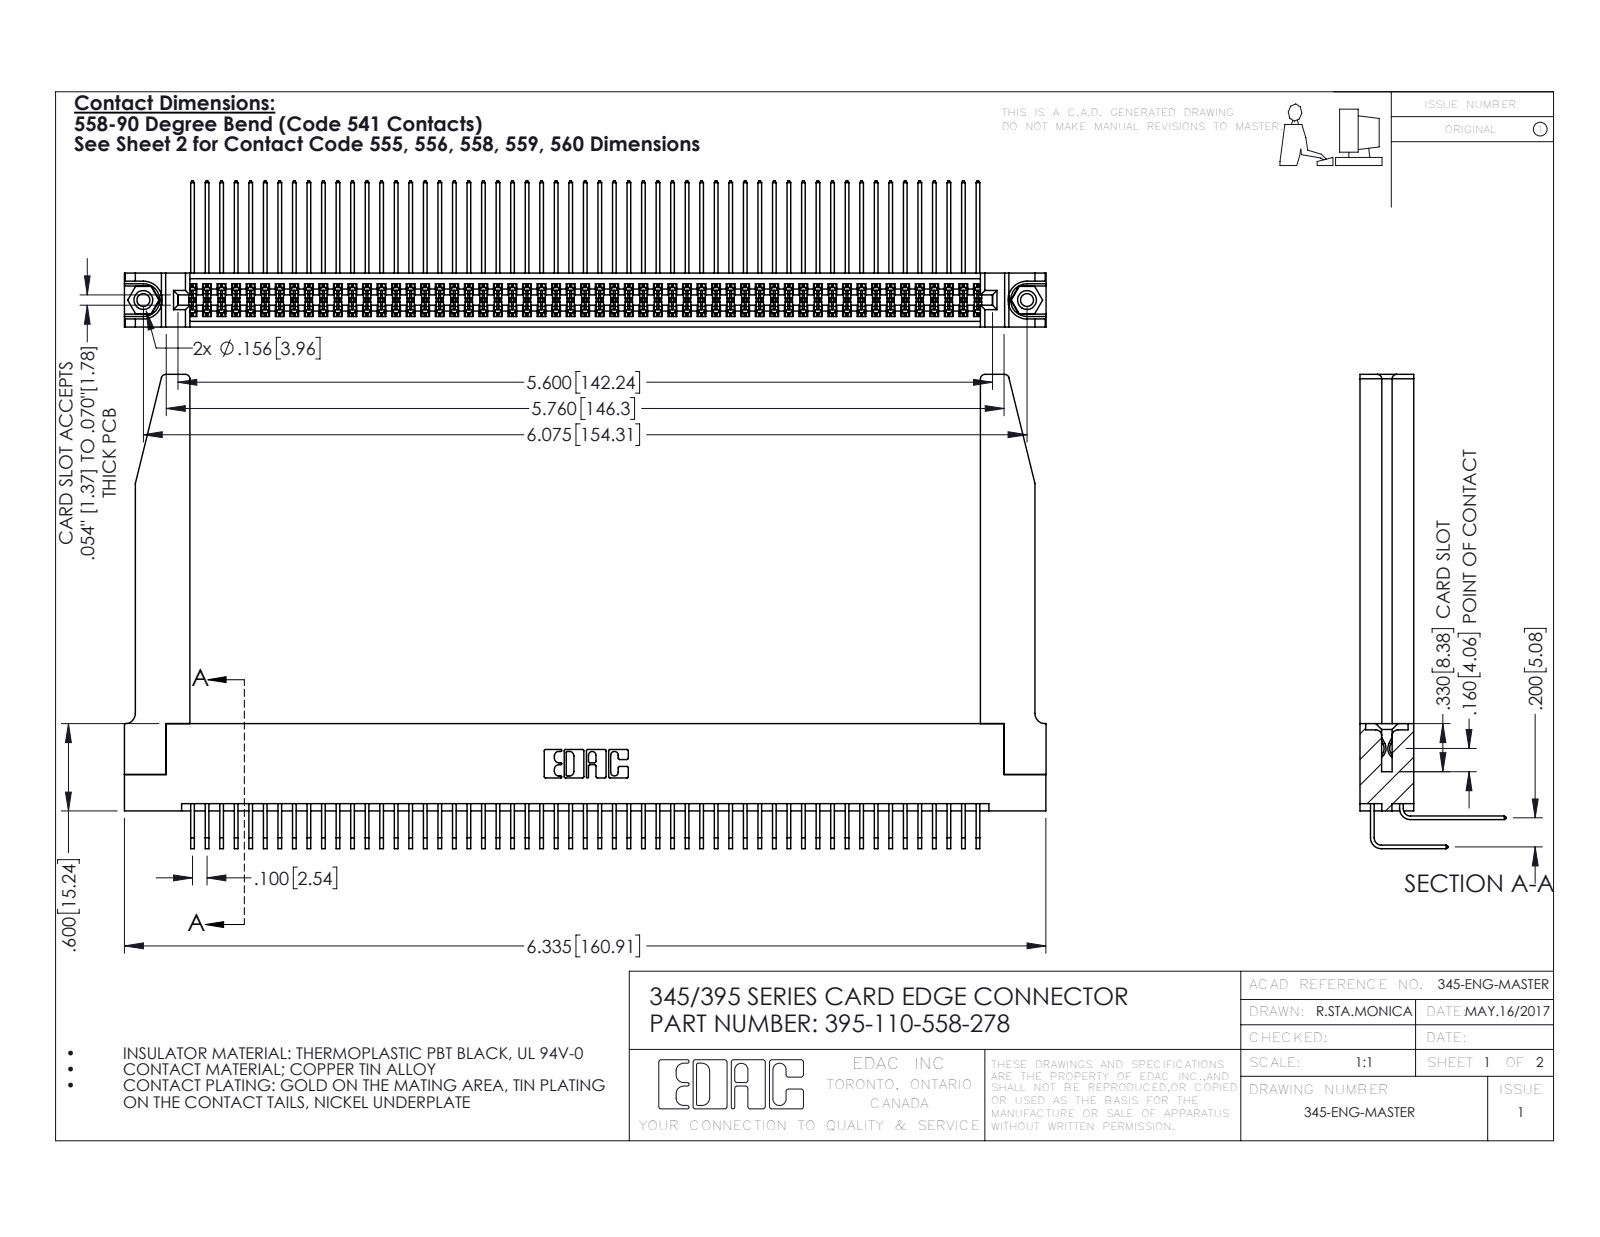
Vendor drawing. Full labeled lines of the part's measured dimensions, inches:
Part name (STEP PRODUCT): 345 Part_Flush Mounting Lugs - 0.156 Dia-TH; 345-220-078_345-220-078; 345-292-001_558 559 Tail - 1; 395-110-558-278 (+2 more)
STEP written by: SolidWorks 2016 (CONFIG_CONTROL_DESIGN)
Units: inches
Bodies: 115 solids, 6080 faces (4072 planar, 1956 cylindrical, 52 other)
Overall size (bounding box): 6.336 × 3.259 × 1.005
Volume: 1.474 in³ · Surface area: 53.16 in²
Round holes (diameter × count): ⌀0.089 ×2, ⌀0.125 ×2, ⌀0.156 ×2, ⌀0.064 ×1
Round bosses / shafts (diameter × count): ⌀0.155 ×2
Partial cylindrical surfaces — rounded edges, fillets, slot ends (radius × count): R0.006 ×165, R0.01 ×22, R0.03 ×8, R0.007 ×6, R0.031 ×6, R0.026 ×3, R0.014 ×2, R0.019 ×2
Main face-to-face distances: 0.072, 0.298, 0.37, 0.2, 0.098, 0.272, 0.025, 0.225, 0.025, 0.285
Hole centre spacings: 0.27, 5.839, 6.075
